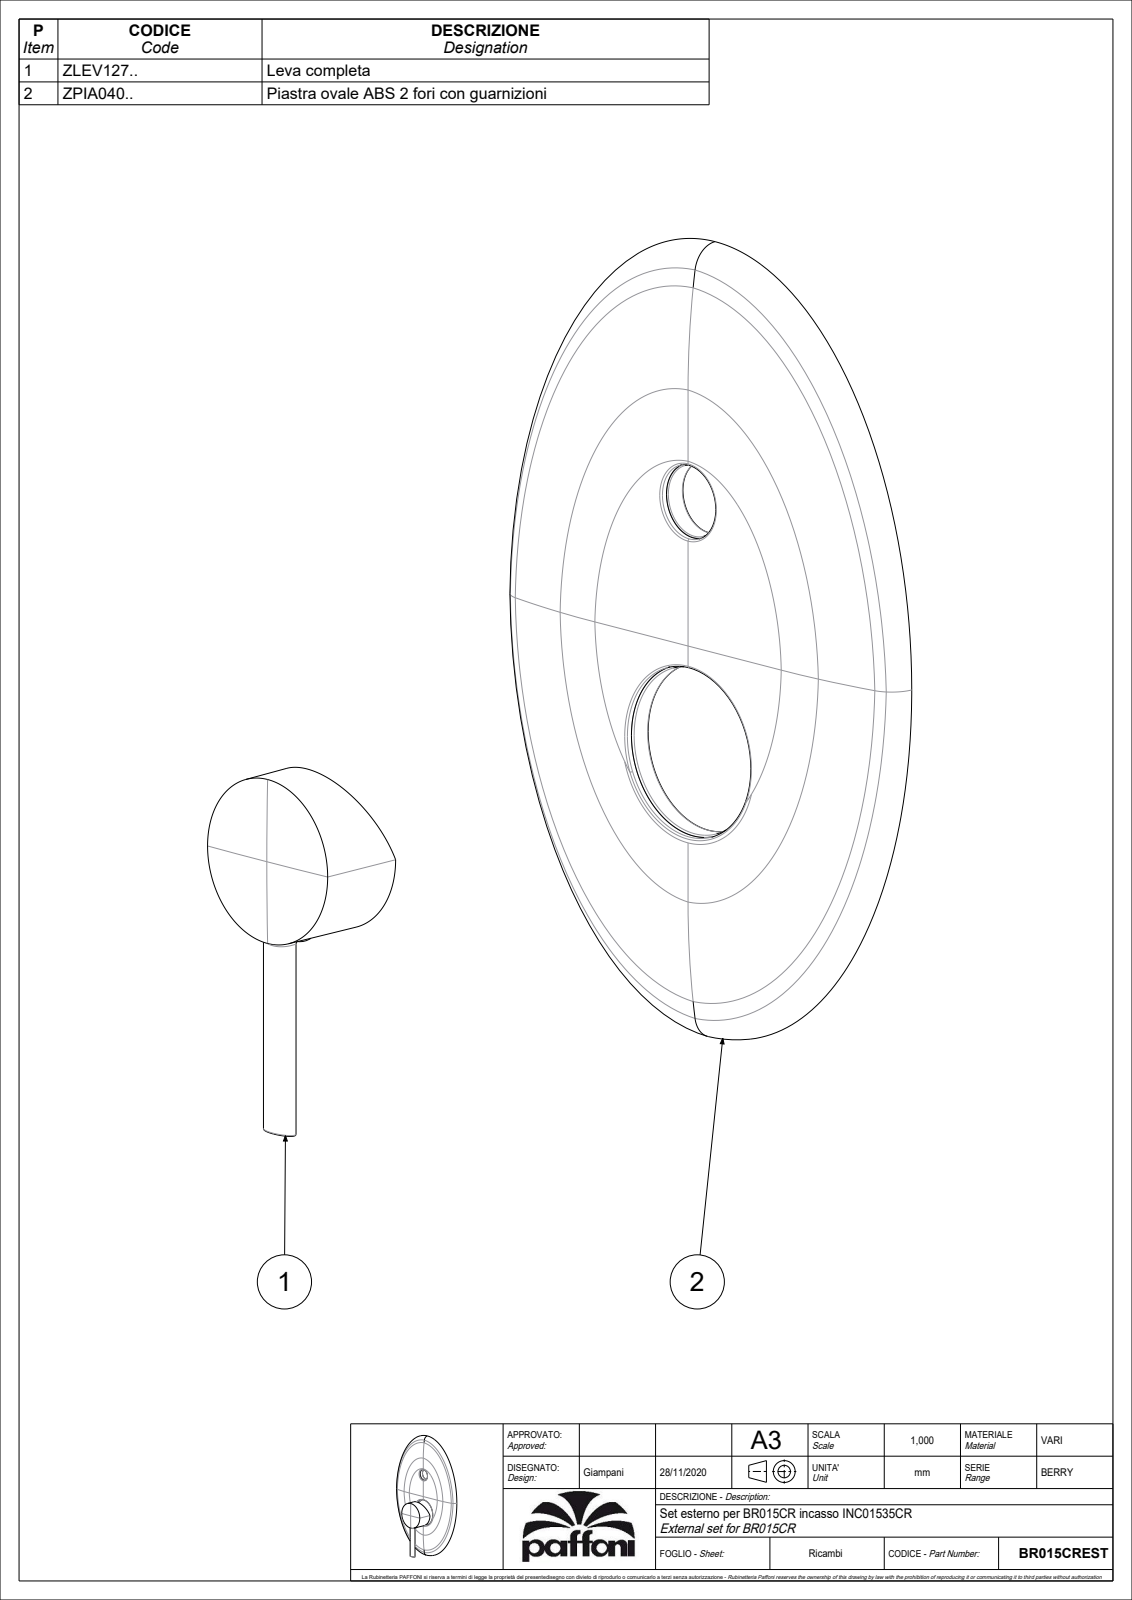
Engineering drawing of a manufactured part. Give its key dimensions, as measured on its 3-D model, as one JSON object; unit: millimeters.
{"part_name": "BR015CREST", "step_written_by": "CREO PARAMETRIC BY PTC INC, 2020044 (CONFIG_CONTROL_DESIGN)", "units": "millimeters", "bodies": {"solids": 2, "faces": 212, "planar": 56, "cylindrical": 54, "other": 102}, "overall_size": [216, 146, 41.63], "volume_mm3": 73058, "surface_area_mm2": 64832, "round_holes": [[3, 1], [3.5, 1], [7.8, 1], [19.2, 1], [20, 1], [21, 1], [23.2, 1], [45, 1], [46, 1]], "round_bosses_or_shafts": [[51, 1], [49, 1], [25, 1], [23, 1], [21.2, 1], [7.6, 1], [5.5, 1]], "partial_cylinders_radius": [[1.25, 4], [0.8, 2], [1, 2], [1.9, 1], [2.5, 1]], "face_to_face_distances": [39, 2, 37, 9.1, 6, 8, 1, 4, 0.55, 8.55], "hole_center_spacings": [0.5, 68]}
